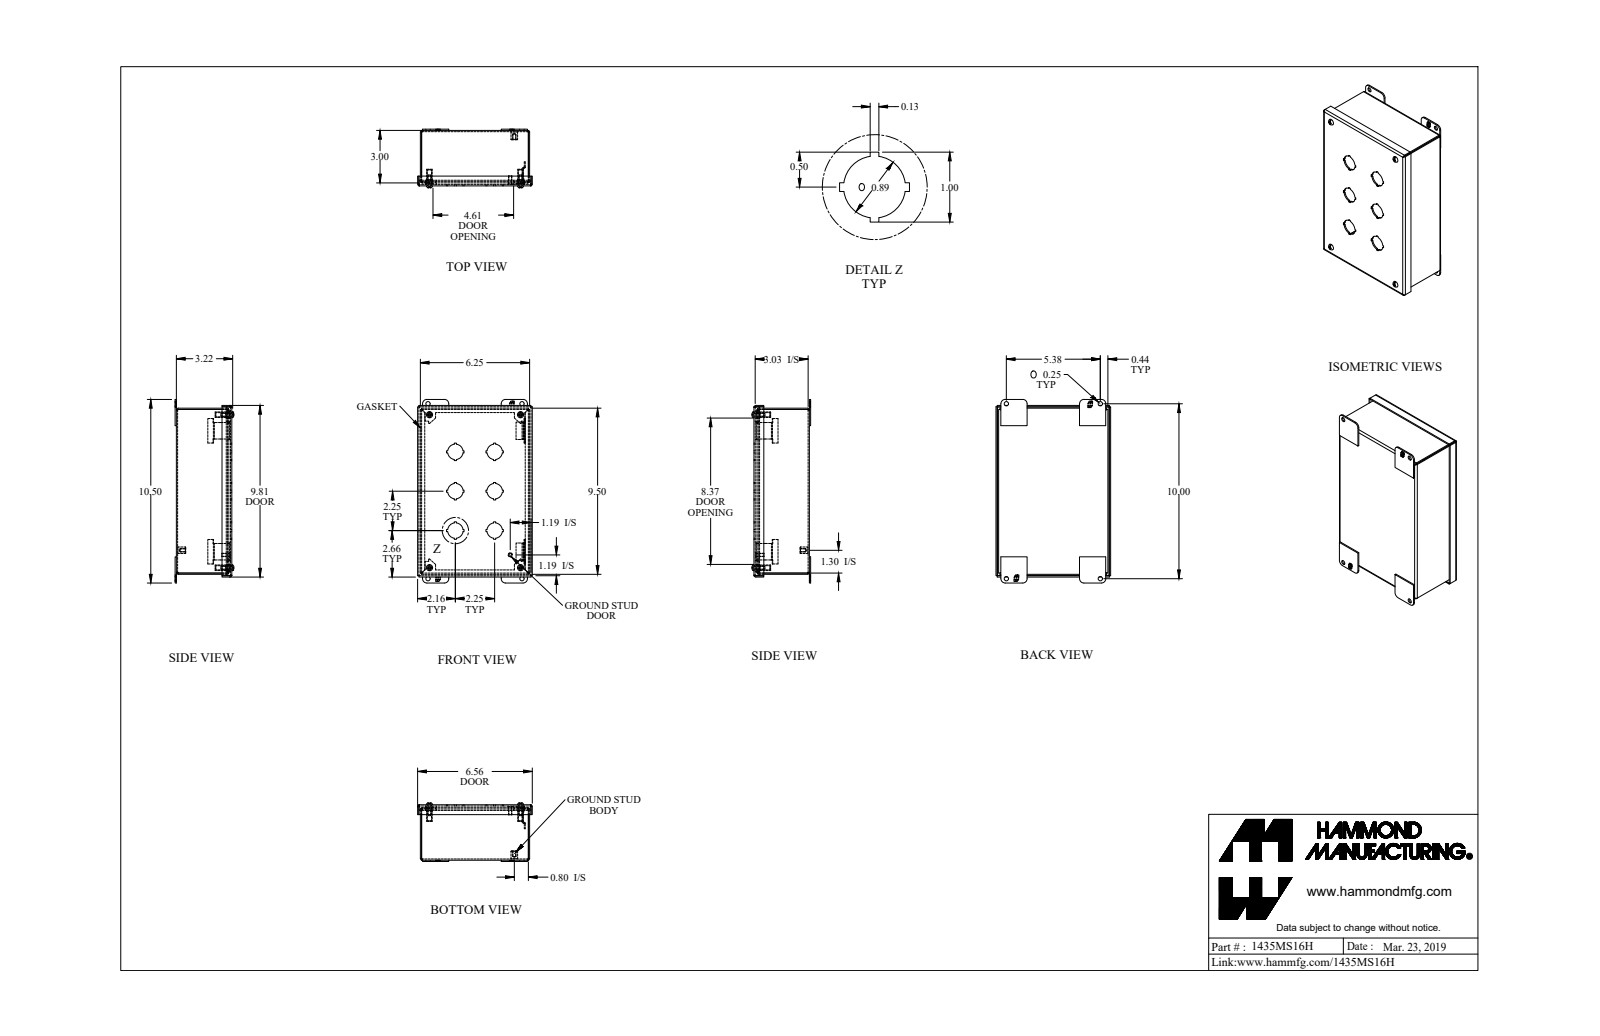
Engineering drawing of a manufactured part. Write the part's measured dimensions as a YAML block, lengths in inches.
part_name: "1435MS16H_Default"
step_written_by: "SolidWorks 2019 (CONFIG_CONTROL_DESIGN)"
units: inches
bodies: {solids: 23, faces: 701, planar: 495, cylindrical: 176, other: 30}
overall_size: [10.5, 6.562, 3.354]
volume: 20.63
surface_area: 546.6
round_holes:
  - {diameter: 0.25, count: 8}
  - {diameter: 0.886, count: 6}
  - {diameter: 0.065, count: 4}
  - {diameter: 0.239, count: 4}
  - {diameter: 0.253, count: 4}
  - {diameter: 0.406, count: 4}
  - {diameter: 0.156, count: 1}
round_bosses_or_shafts:
  - {diameter: 0.19, count: 5}
  - {diameter: 0.406, count: 4}
  - {diameter: 0.315, count: 4}
  - {diameter: 0.148, count: 4}
  - {diameter: 0.375, count: 1}
  - {diameter: 0.25, count: 1}
partial_cylinders:
  - {radius: 0.036, count: 12}
  - {radius: 0.108, count: 12}
  - {radius: 0.25, count: 8}
  - {radius: 0.029, count: 4}
  - {radius: 0.086, count: 4}
  - {radius: 0.171, count: 4}
face_to_face_distances: [0.072, 3.1, 3.172, 3.028, 6.178, 9.428, 6.25, 6.106, 0.156, 6.334]
hole_center_spacings: [5.211, 5.212, 8.749, 8.75, 9.375, 2.25, 10.183, 10.183]
